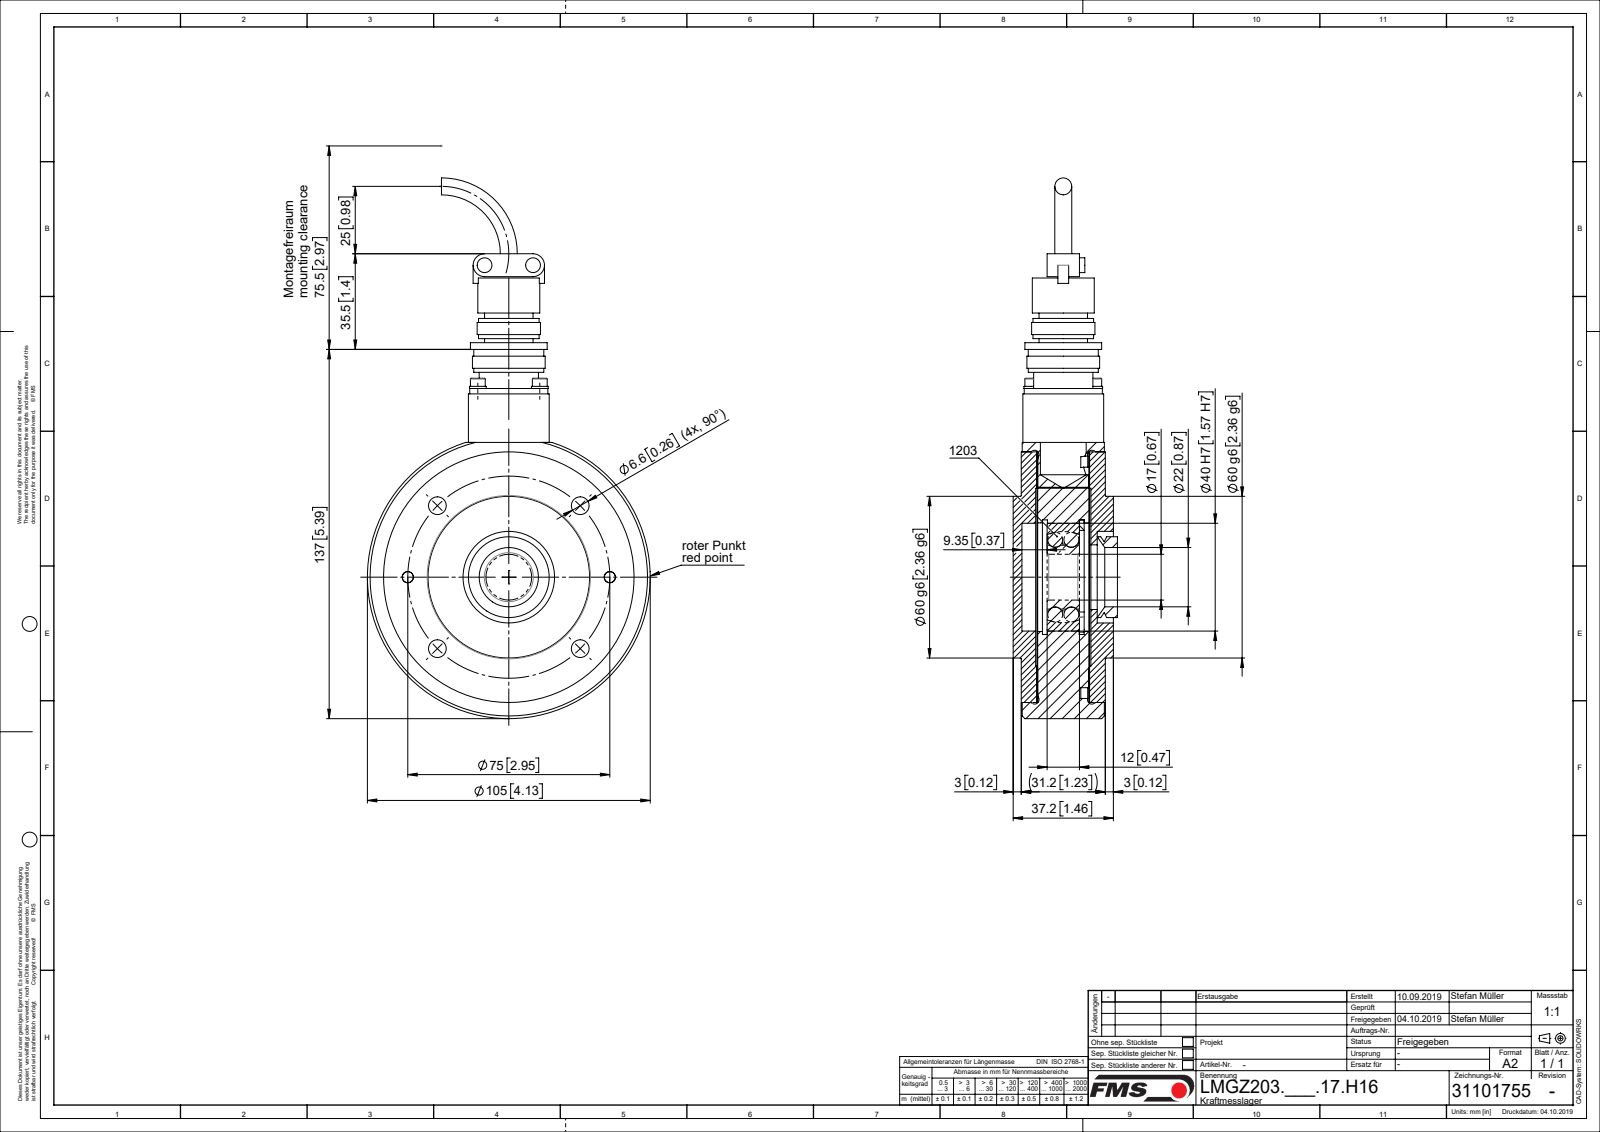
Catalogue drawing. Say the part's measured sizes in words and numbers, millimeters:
The part is named "ZEICHNUNG3; L50005; L4795904; L47958(1) (+8 more)". Its 3-D file was written by "Mechanical Desktop 2007 (CONFIG_CONTROL_DESIGN)". It is 20 solids with 383 faces: 114 planar, 225 cylindrical and 44 other. Overall it measures 200.65 by 105 by 37.2 millimeters. Its volume is 286 820 cubic millimeters and its surface area 103 643 square millimeters. Round holes: 4 of diameter 2.6, 4 of diameter 3.2, 4 of diameter 3.4, 4 of diameter 6.6, 2 of diameter 4, 2 of diameter 5.3, 2 of diameter 5.5, 2 of diameter 10, 1 of diameter 17, 1 of diameter 22, 1 of diameter 23, 1 of diameter 24. Round bosses or shafts: 6 of diameter 5.5, 4 of diameter 6.2, 4 of diameter 3, 4 of diameter 2.5, 2 of diameter 8, 2 of diameter 5, 1 of diameter 105, 1 of diameter 93. Partial cylindrical surfaces (rounded edges, fillets, slot ends): 2 of radius 4.25, 1 of radius 2. The main face-to-face distances are 19.25, 19, 5.85, 25.1, 6.1, 25.35, 19.5, 3, 20, 0.5. The hole center spacings are 37.5, 16.26, 23, 28.7, 53.04, 69.3, 32.53, 75.01.
